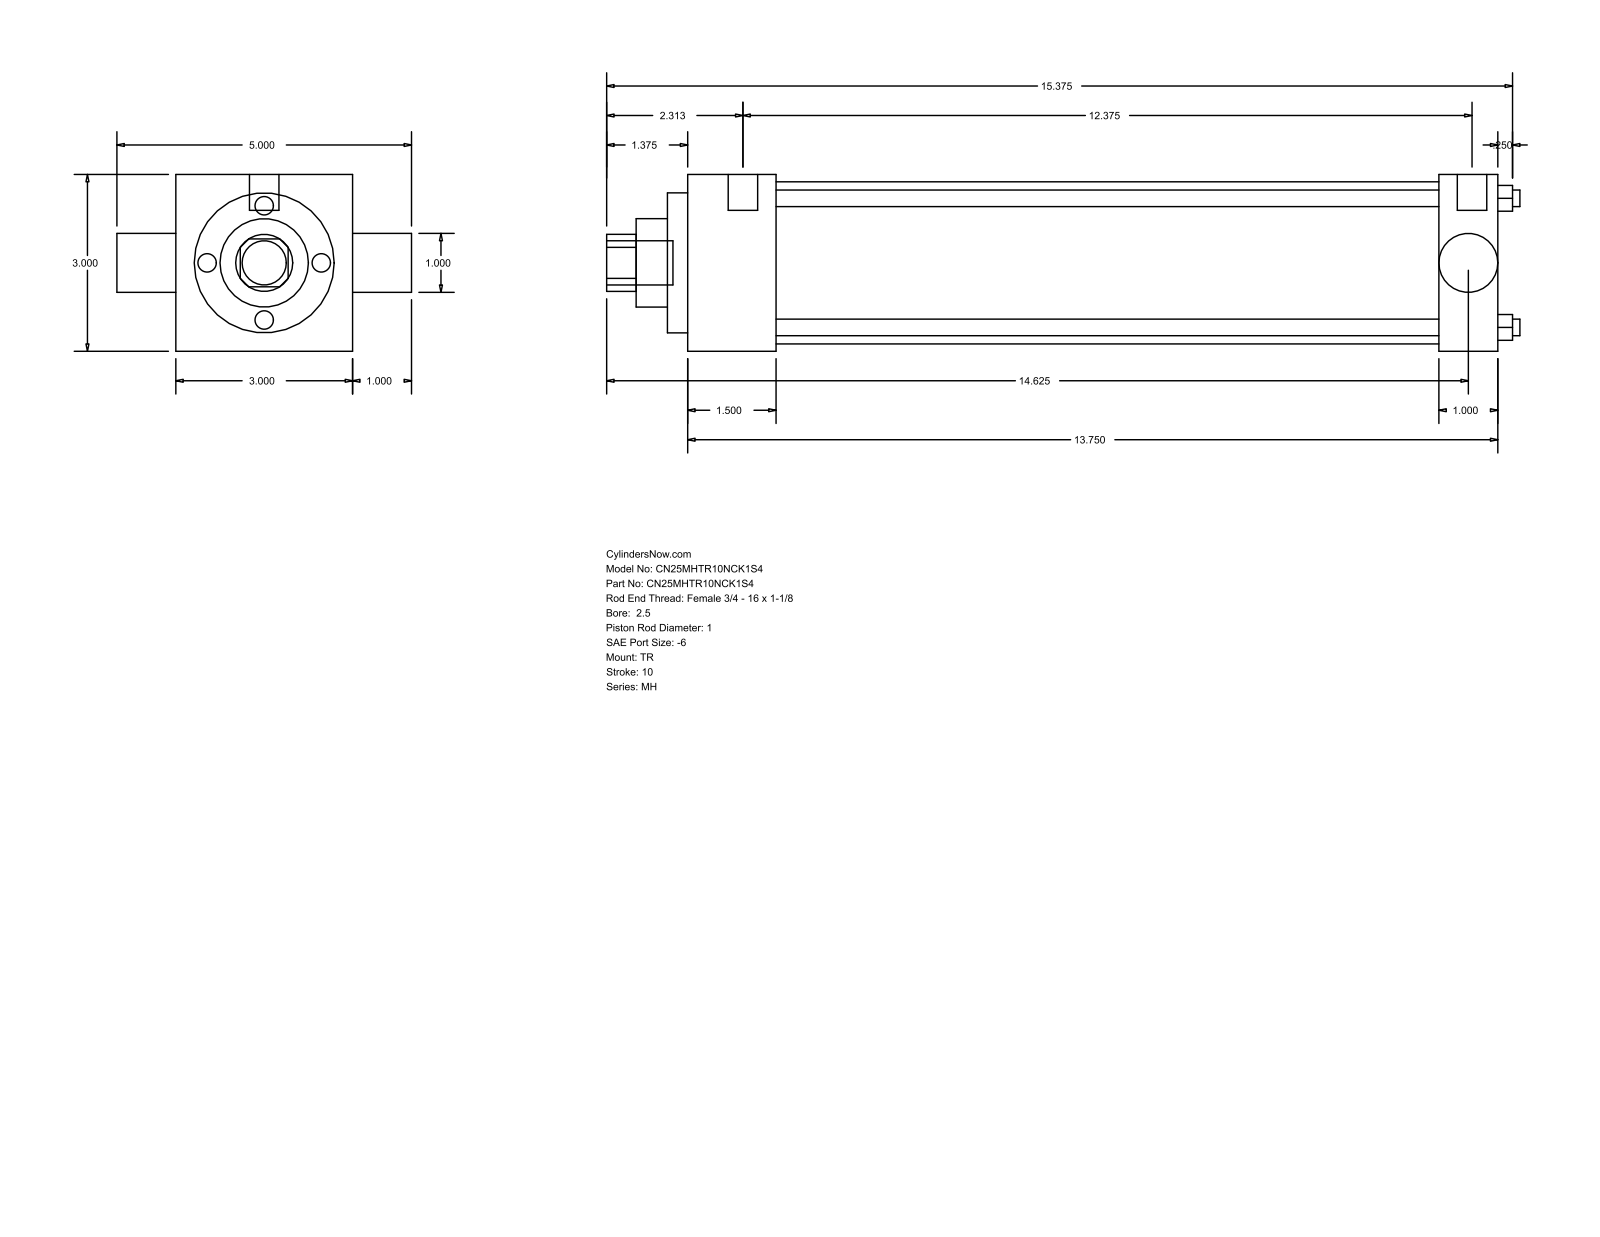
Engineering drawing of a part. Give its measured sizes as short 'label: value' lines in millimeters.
name: MH_TR__0250_1
written by: GSSL Pune (CONFIG_CONTROL_DESIGN)
unit: mm
bodies: 0 solids, 86 faces (61 planar, 25 cylindrical, 0 other)
size: 393.7 × 127 × 76.2
holes: 4× ⌀7.14, 1× ⌀25.35, 1× ⌀25.4, 1× ⌀38.1, 1× ⌀60.33, 1× ⌀69.85
bosses: 3× ⌀5.56, 2× ⌀12.7, 1× ⌀19.05
rounds: 1× R12.29
face distances: 76.2, 349.26, 38.11, 311.15, 323.85, 285.74, 25.41, 8.73, 46.84, 332.58
hole spacings: 39.33, 55.62, 78.66
